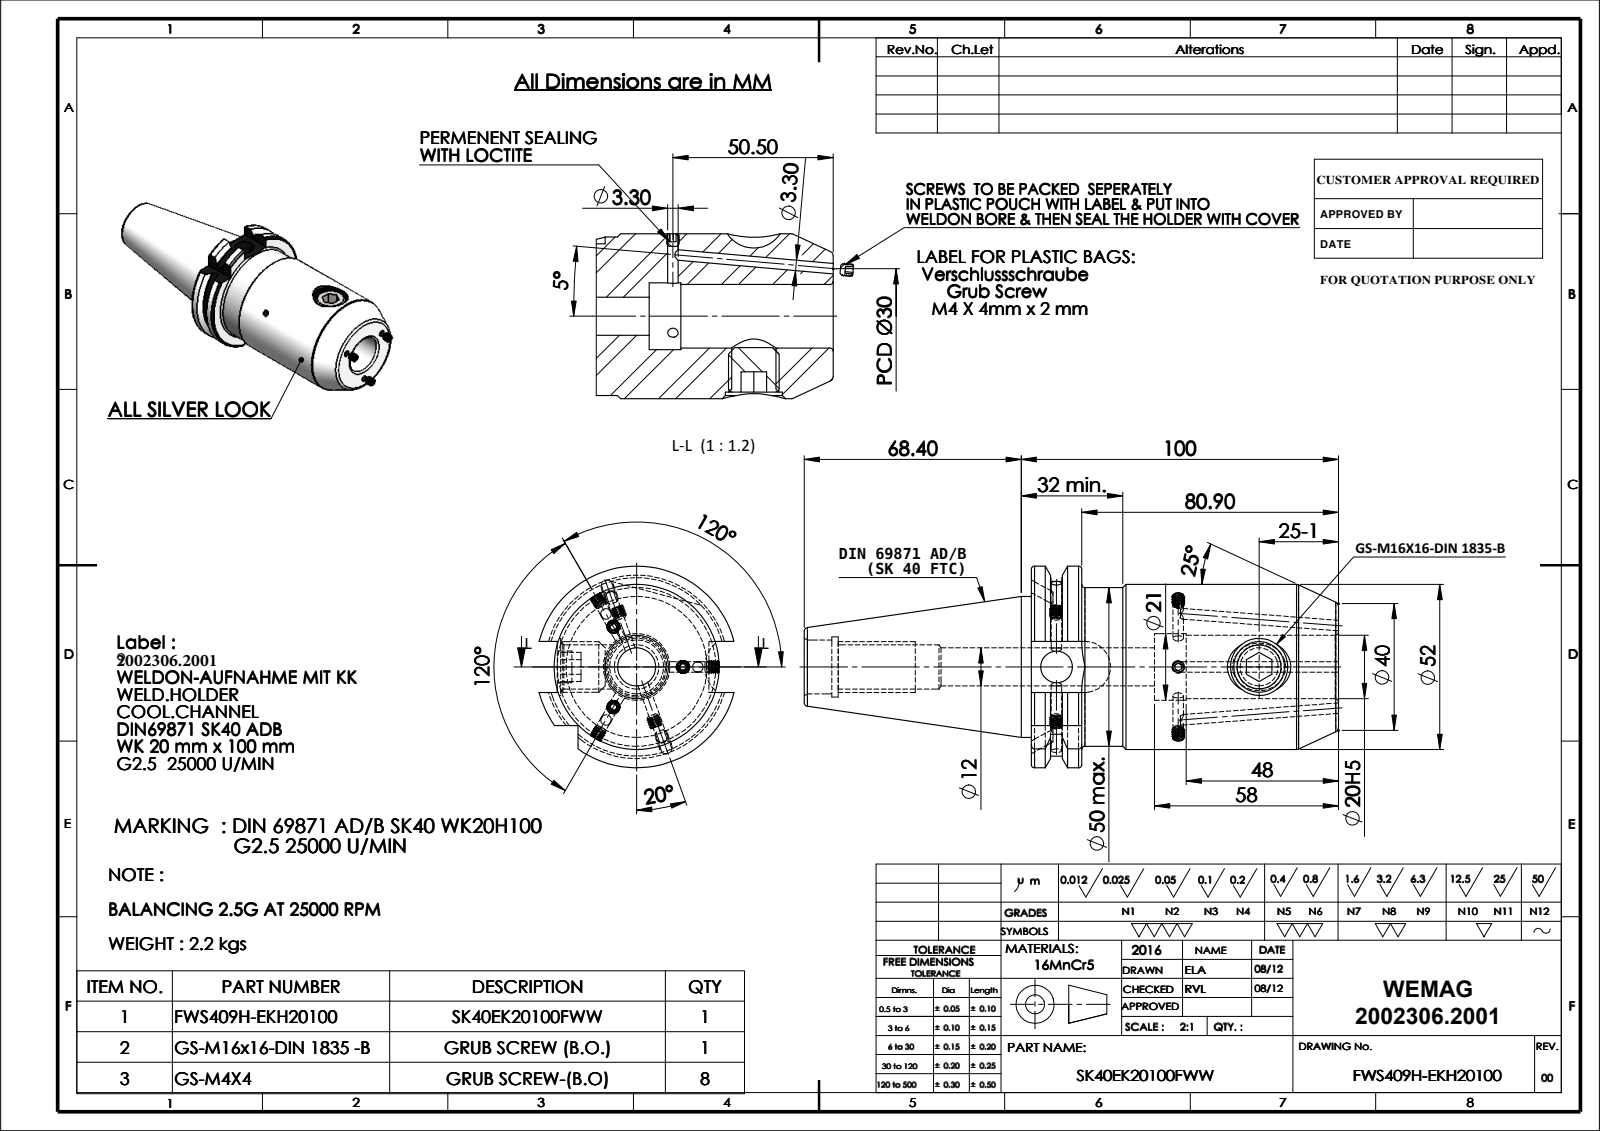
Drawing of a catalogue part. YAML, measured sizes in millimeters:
part_name: "SK400EK20100FWW; GS-M4X4_DIN 913 - M4 x 10-N; 91406-WK220100; M16X16_ISO 4026 - M16 x 10-N"
step_written_by: "SolidWorks 2009 (CONFIG_CONTROL_DESIGN)"
units: millimeters
bodies: {solids: 10, faces: 529, planar: 119, cylindrical: 135, other: 275}
overall_size: [174.84, 63.55, 61.48]
volume: 240346
surface_area: 42441
round_holes:
  - {diameter: 3.3, count: 7}
  - {diameter: 14, count: 2}
  - {diameter: 10, count: 1}
  - {diameter: 12, count: 1}
  - {diameter: 17, count: 1}
  - {diameter: 18, count: 1}
  - {diameter: 19, count: 1}
  - {diameter: 20, count: 1}
  - {diameter: 21, count: 1}
round_bosses_or_shafts:
  - {diameter: 4, count: 8}
  - {diameter: 52, count: 1}
  - {diameter: 50, count: 1}
  - {diameter: 44.45, count: 1}
  - {diameter: 16, count: 1}
partial_cylinders:
  - {radius: 8.05, count: 1}
  - {radius: 28.12, count: 1}
  - {radius: 31.77, count: 1}
face_to_face_distances: [96.8, 15.9, 80.9, 38.8, 22.9, 58, 47.8, 16.1, 3.5, 46.7]
hole_center_spacings: [25.5, 38.35, 63.85]
